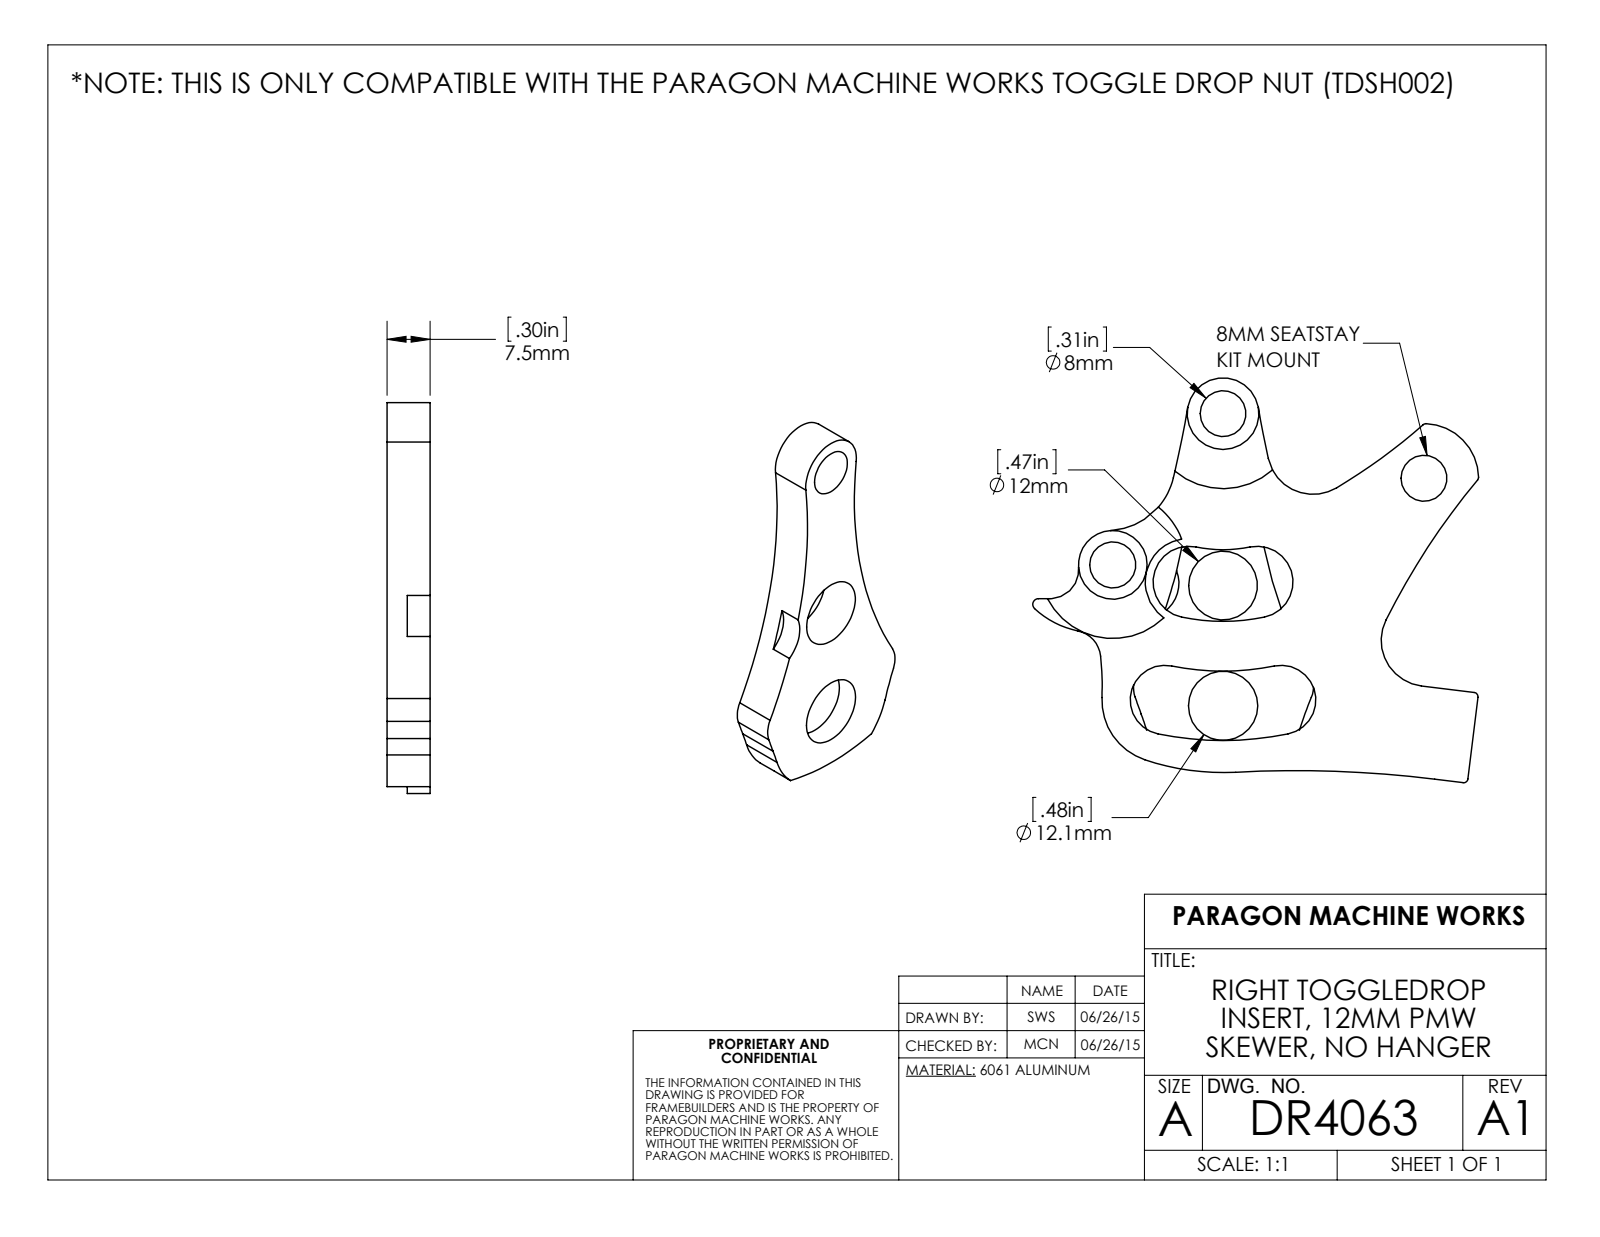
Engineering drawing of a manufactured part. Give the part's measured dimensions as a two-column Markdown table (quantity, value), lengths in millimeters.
| quantity | value |
| --- | --- |
| part name | DR4063 |
| STEP written by | SolidWorks 2015 (AUTOMOTIVE_DESIGN) |
| units | millimeters |
| bodies | 1 solid, 31 faces (6 planar, 25 cylindrical, 0 other) |
| overall size | 68.25 × 31.44 × 7.5 |
| volume | 6 399 mm³ |
| surface area | 3 943 mm² |
| round holes (diameter × count) | 8.1 × 1, 12 × 1, 12.1 × 1 |
| partial cylindrical surfaces (radius × count) | 5 × 2, 76.25 × 2, 6.1 × 1, 6.25 × 1, 10 × 1, 14 × 1, 42.2 × 1, 75 × 1 |
| main face-to-face distances | 7.5, 4, 3.5, 20 |
| hole center spacings | 21, 30, 51 |
